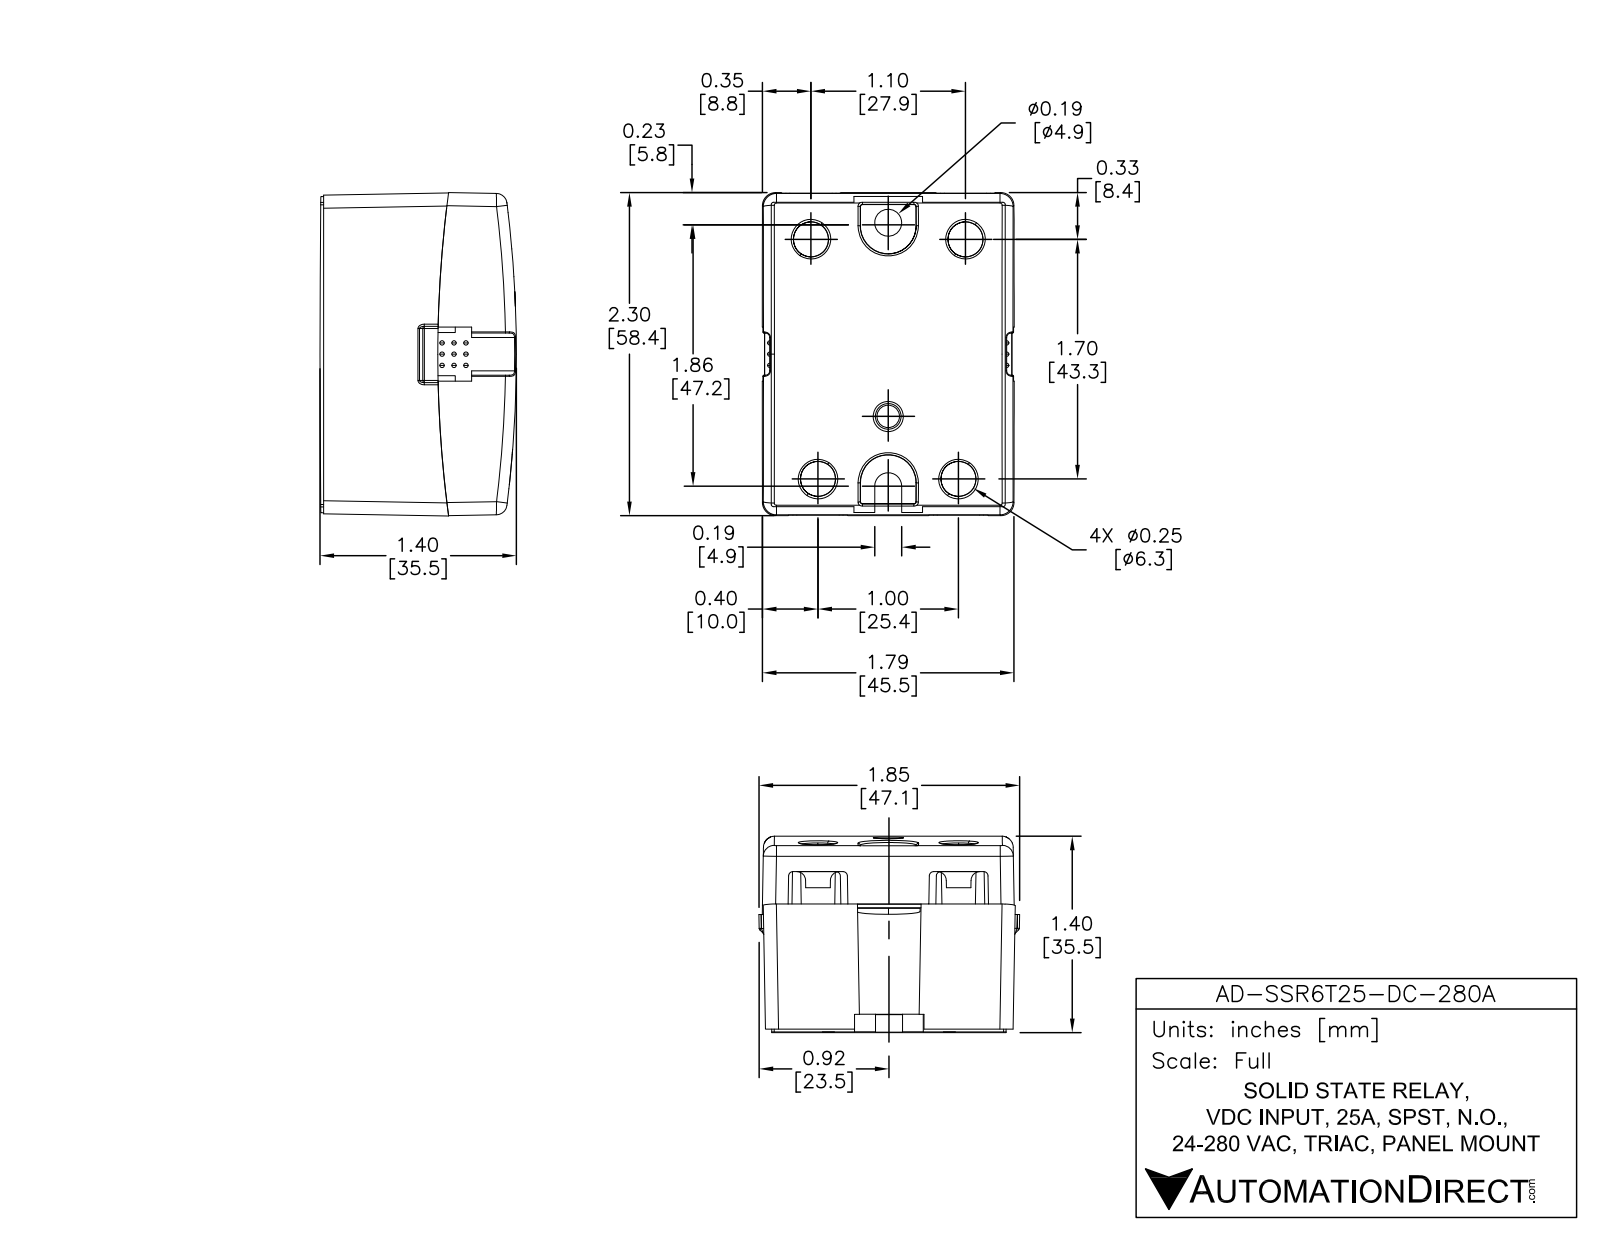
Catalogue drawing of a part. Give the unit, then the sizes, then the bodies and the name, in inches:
Units: inches
Overall size (bounding box): 2.3 × 1.79 × 1.4
Round holes (diameter × count): ⌀0.25 ×4, ⌀0.19 ×1
Round bosses / shafts (diameter × count): ⌀0.4 ×2, ⌀0.35 ×2, ⌀0.3 ×2, ⌀0.25 ×2, ⌀0.2 ×2, ⌀0.2 ×2
Partial cylindrical surfaces — rounded edges, fillets, slot ends (radius × count): R0.03 ×6, R0.01 ×4, R0.04 ×4, R0.5 ×4, R0.194 ×2, R0.095 ×1, R0.5 ×1, R0.5 ×1
Main face-to-face distances: 1.79, 2.3, 1.166, 0.25, 0.916, 0.671, 1.059, 0.5, 1.8, 0.08
Hole centre spacings: 0.556, 0.565, 1, 1.1, 1.7, 1.701, 1.876, 1.879
Volume: 5.14 in³ · Surface area: 26.41 in²
Bodies: 3 solids, 251 faces (145 planar, 95 cylindrical, 11 other)
Part name (STEP PRODUCT): AD-SSR6T25-DC-280A
STEP written by: SolidWorks 2013 (AUTOMOTIVE_DESIGN)
